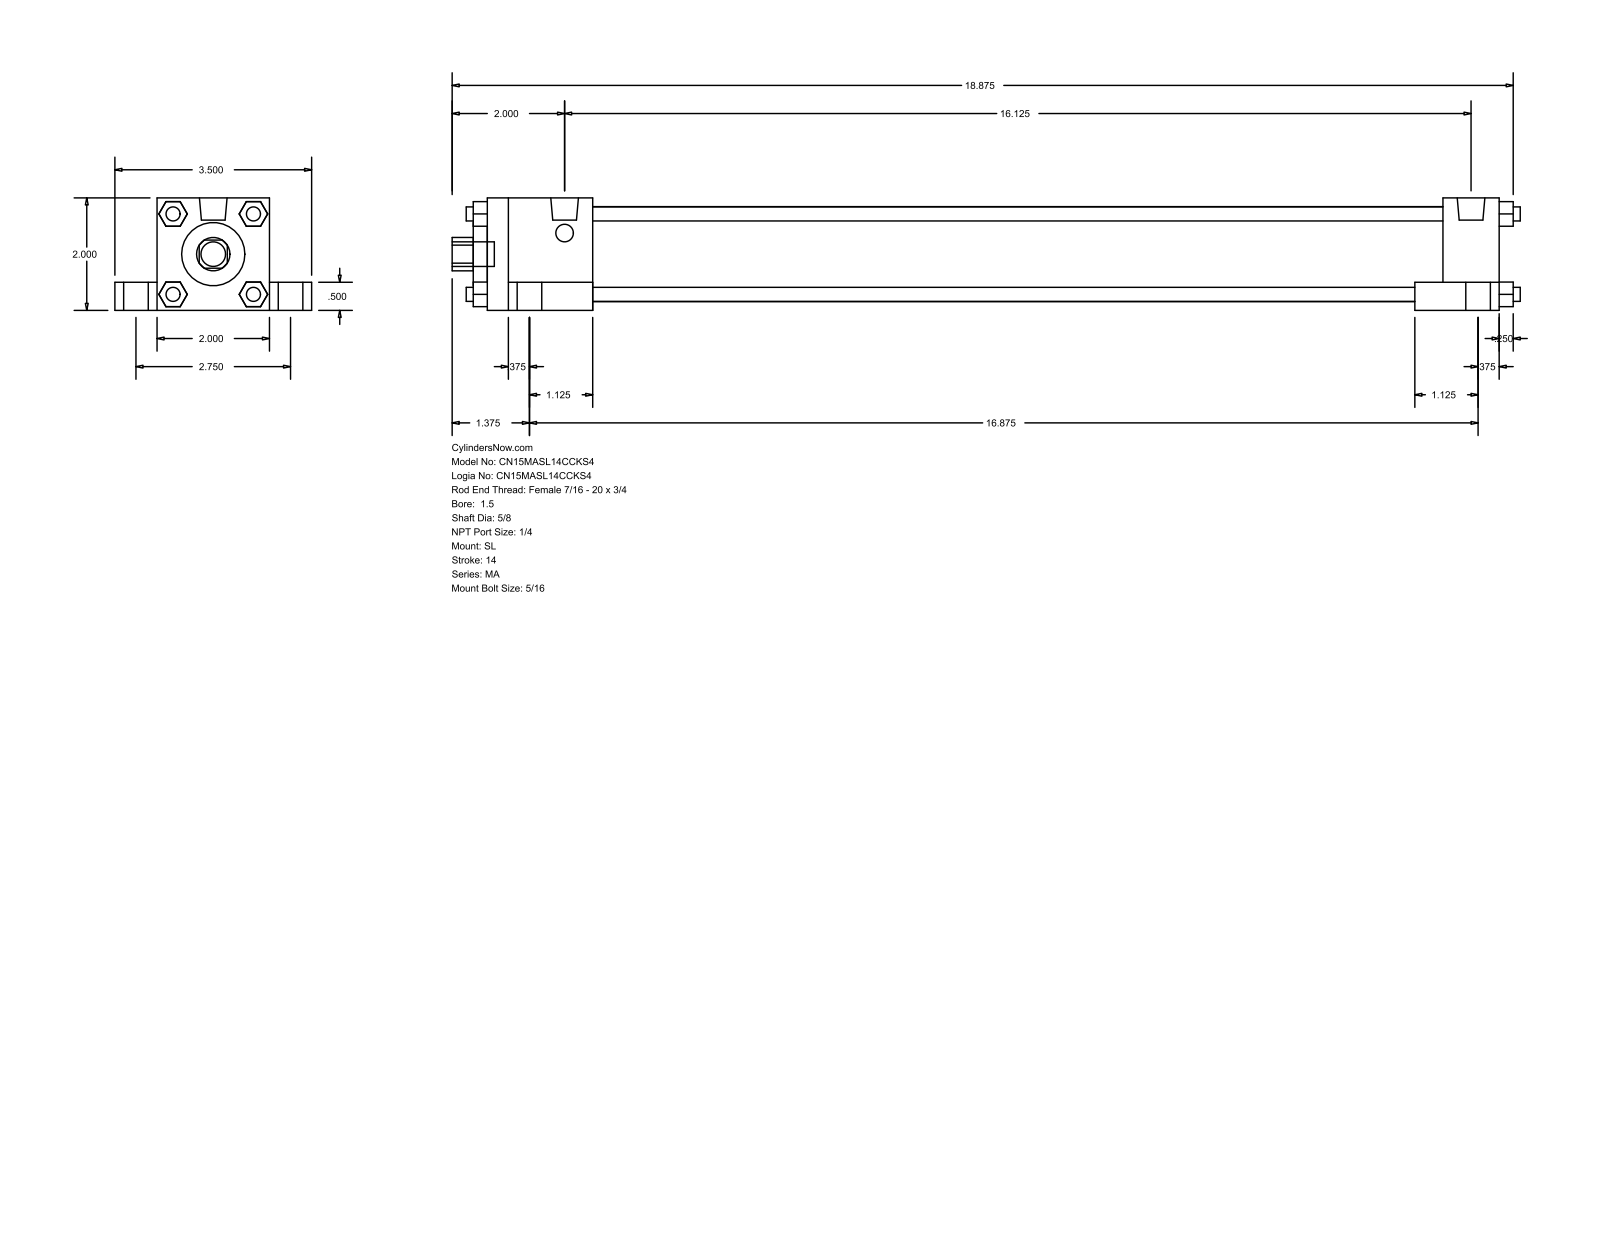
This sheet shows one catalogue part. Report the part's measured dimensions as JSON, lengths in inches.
{"part_name": "MA_SL__0150_0.625", "step_written_by": "GSSL Pune (CONFIG_CONTROL_DESIGN)", "units": "inches", "bodies": {"solids": 0, "faces": 148, "planar": 112, "cylindrical": 36, "other": 0}, "overall_size": [19, 3.5, 2], "round_holes": [[0.625, 1], [1.125, 1], [1.69, 1]], "round_bosses_or_shafts": [[0.437, 5], [0.687, 4], [0.313, 4], [0.25, 4], [0.492, 2]], "partial_cylinders_radius": [[0.297, 1]], "face_to_face_distances": [2, 0.75, 1.5, 0.5, 2.75, 18, 0.375, 17, 1, 1.875]}
